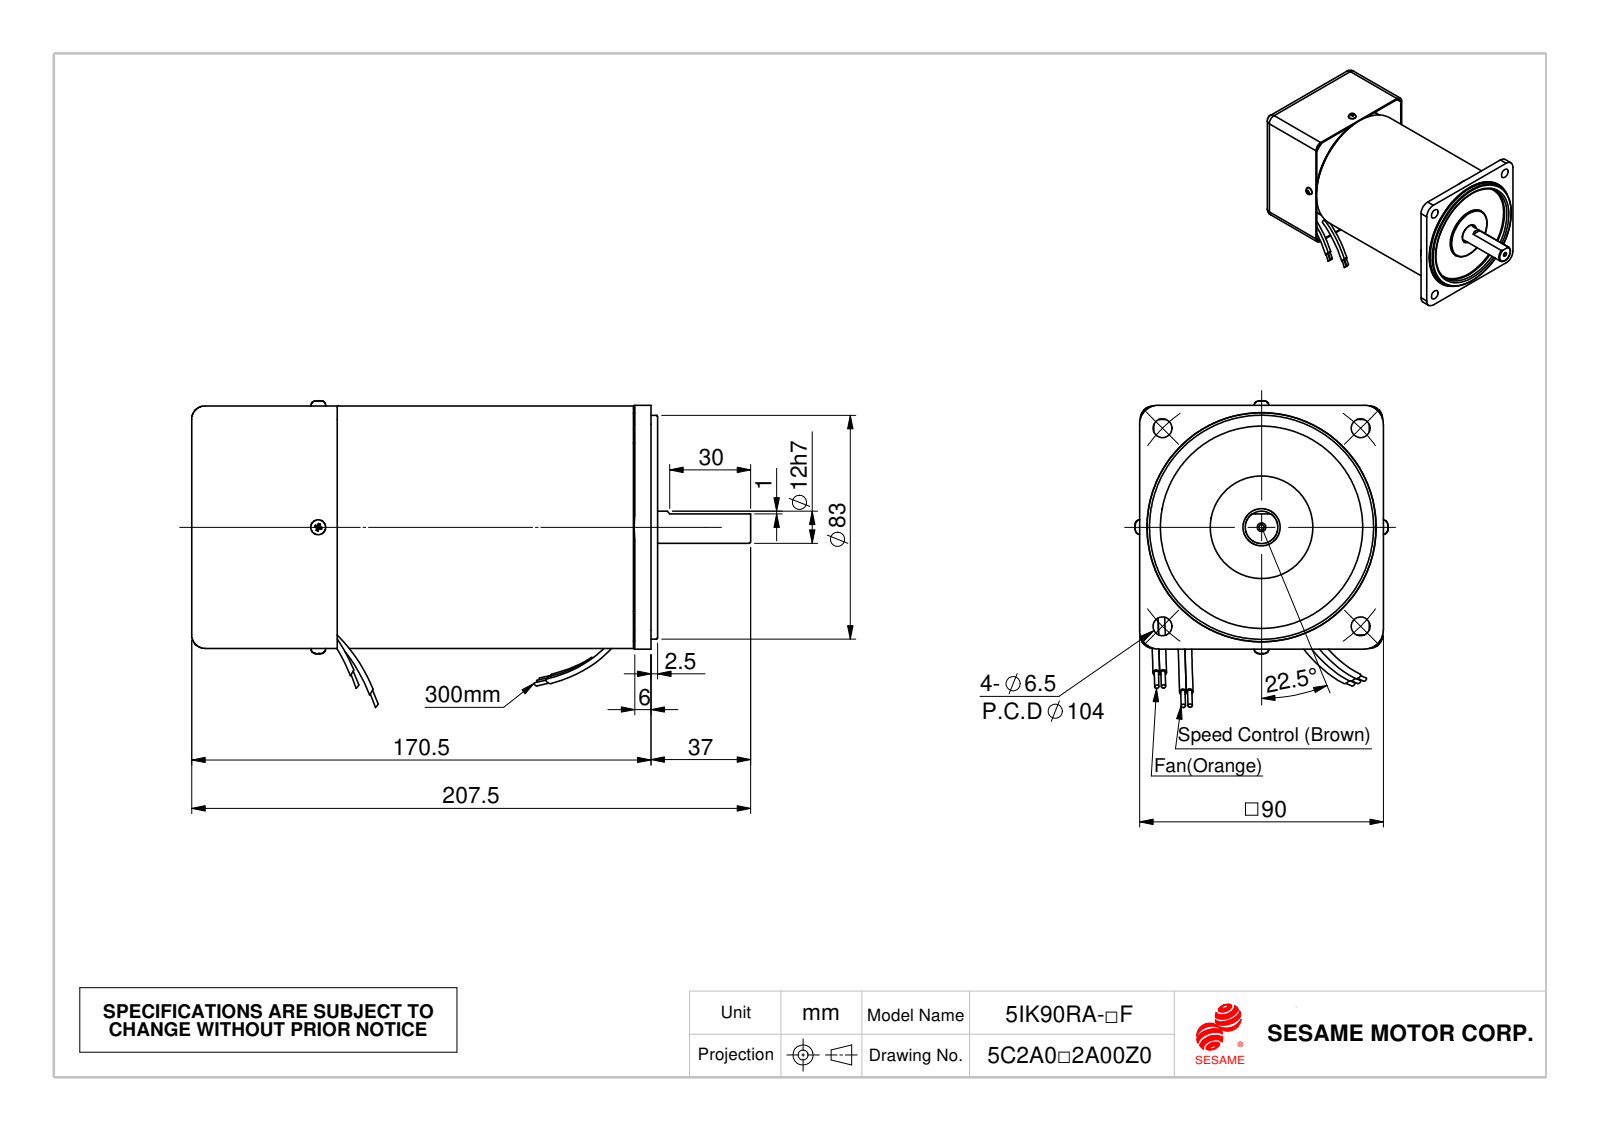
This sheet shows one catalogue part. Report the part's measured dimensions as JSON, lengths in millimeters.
{"part_name": "線扣; M590-R-F; 90A_1成品; 獨立風扇220V 3K22200000", "step_written_by": "SolidWorks 2010 (CONFIG_CONTROL_DESIGN)", "units": "millimeters", "bodies": {"solids": 16, "faces": 437, "planar": 171, "cylindrical": 171, "other": 95}, "overall_size": [207.5, 113.87, 93.92], "volume_mm3": 1050000, "surface_area_mm2": 137156, "round_holes": [[2.5, 5], [7, 4], [1.5, 2], [3, 2], [2, 1], [9.5, 1], [13.7, 1], [16, 1], [26, 1], [58.1, 1], [64.97, 1], [75, 1]], "round_bosses_or_shafts": [[11, 3], [5.5, 2], [90, 1], [87, 1], [86, 1], [84.15, 1], [84, 1], [83, 1]], "partial_cylinders_radius": [[0.3, 16], [4, 8], [5, 8], [2, 4], [7, 4], [26.9, 1], [44.58, 1]], "face_to_face_distances": [1, 89, 4, 5, 84, 85, 90, 88, 139.9, 29], "hole_center_spacings": [38.18, 52, 73.18, 73.54, 1.25, 26.5, 104, 2.5]}
